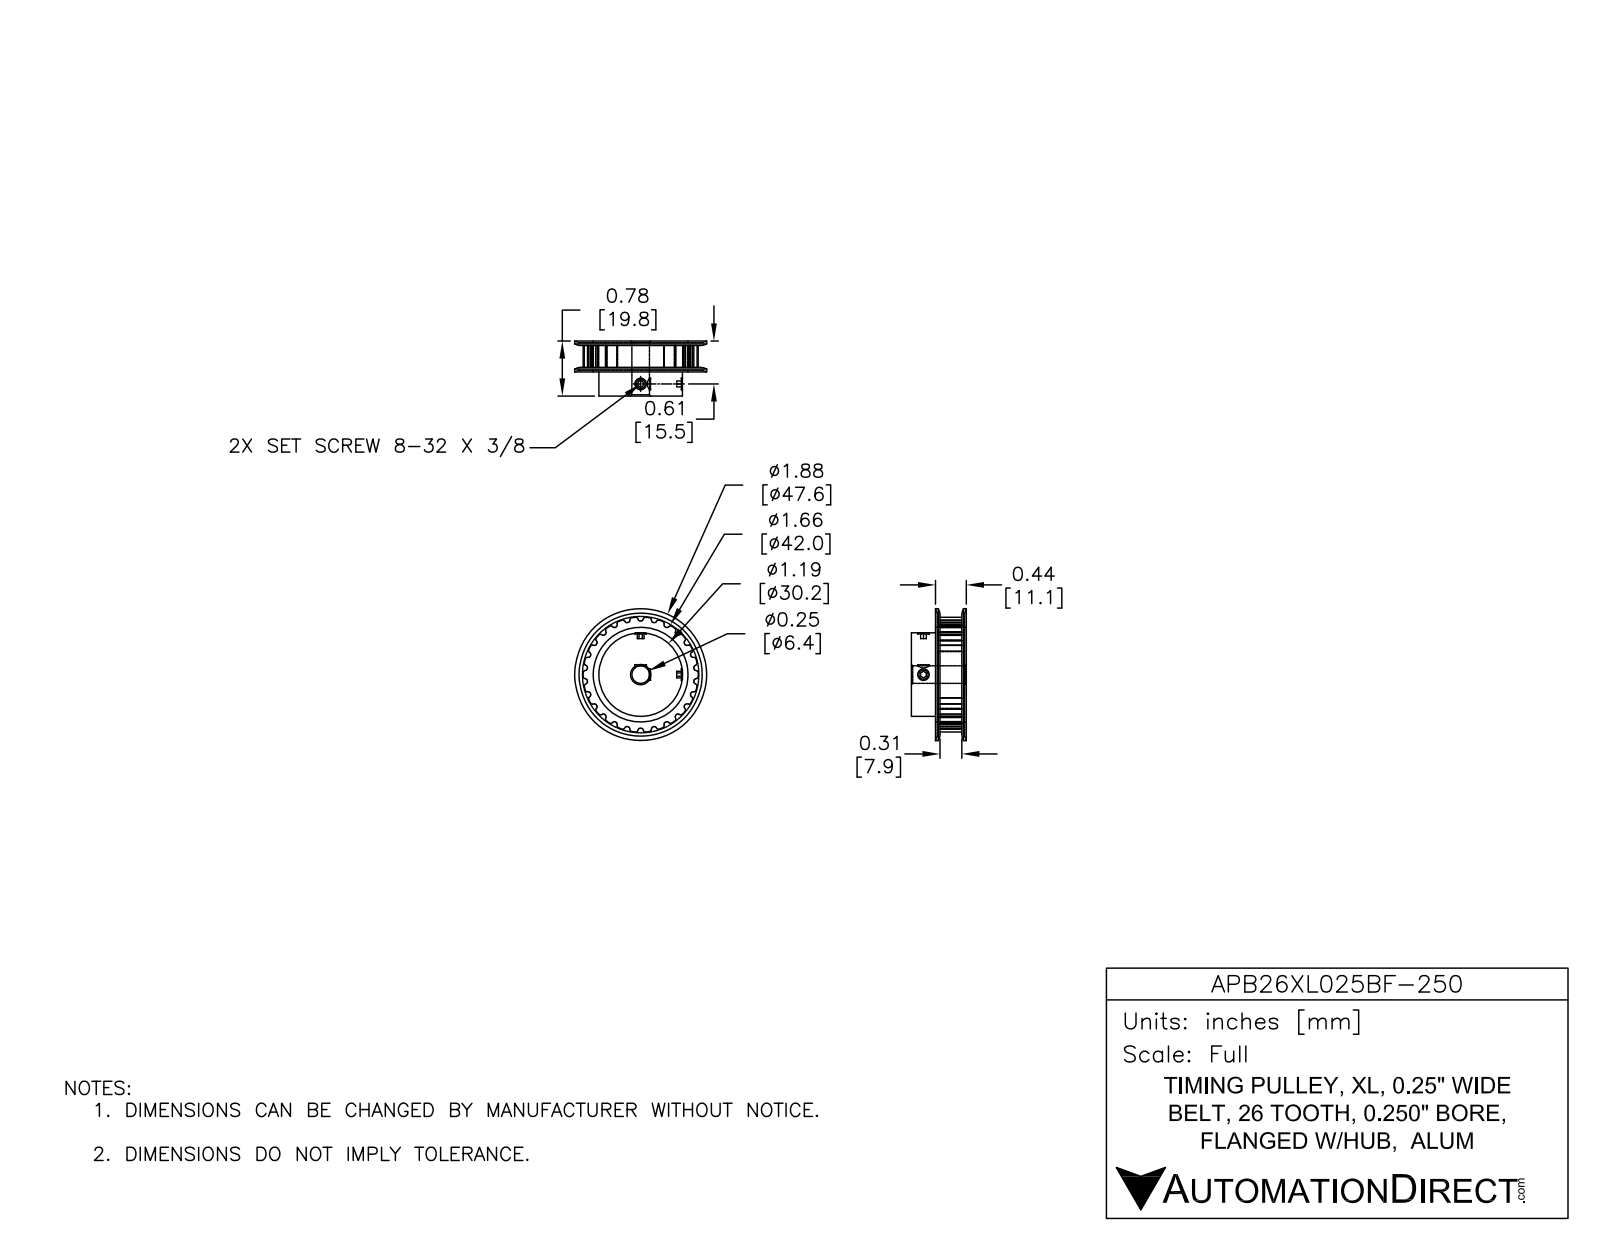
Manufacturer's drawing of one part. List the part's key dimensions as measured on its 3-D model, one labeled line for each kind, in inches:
Part name (STEP PRODUCT): APB26XL025BF-250
STEP written by: SolidWorks 2014 (AUTOMOTIVE_DESIGN)
Units: inches
Bodies: 1 solid, 265 faces (84 planar, 159 cylindrical, 22 other)
Overall size (bounding box): 1.875 × 1.875 × 0.781
Volume: 1.202 in³ · Surface area: 11.72 in²
Round holes (diameter × count): ⌀0.088 ×2, ⌀0.25 ×1
Round bosses / shafts (diameter × count): ⌀1.188 ×1
Partial cylindrical surfaces — rounded edges, fillets, slot ends (radius × count): R0.015 ×104, R0.762 ×1
Main face-to-face distances: 0.033, 0.407, 0.375, 0.781, 0.748, 0.374, 0.032, 0.343, 0.598, 1.635
